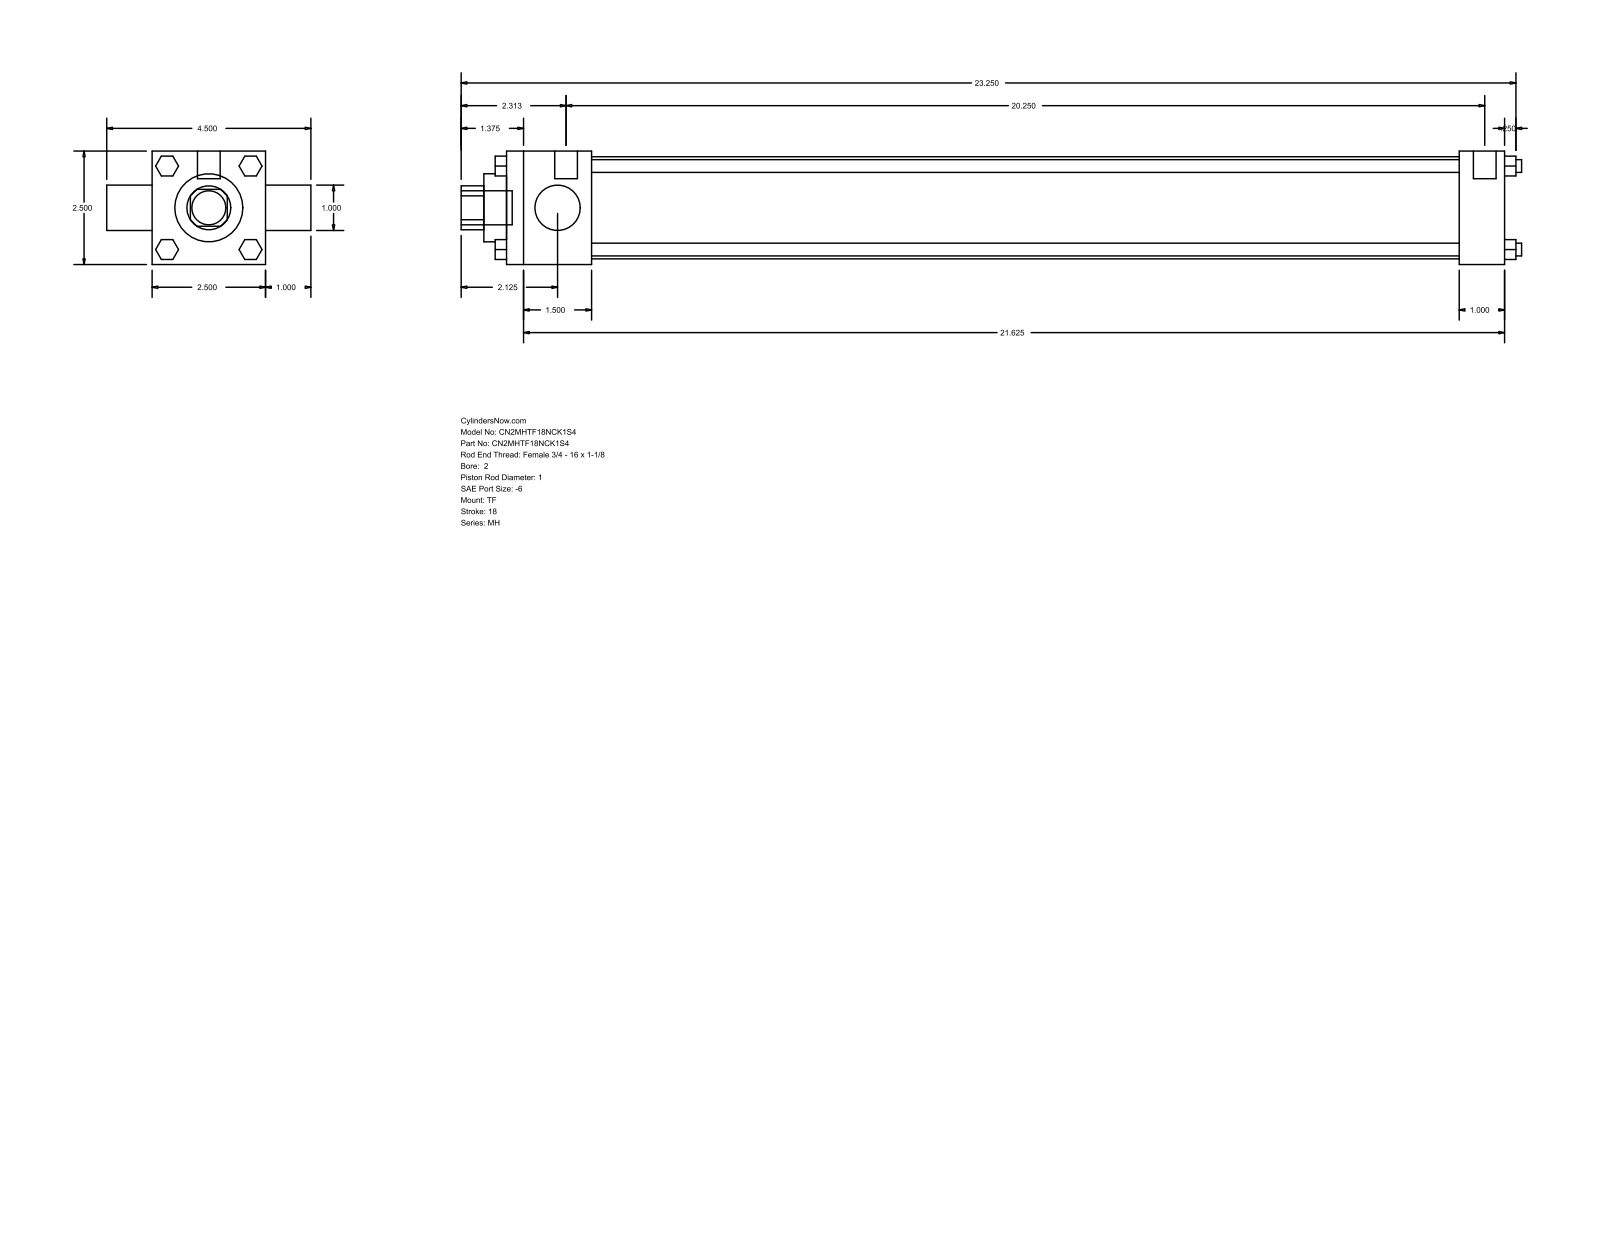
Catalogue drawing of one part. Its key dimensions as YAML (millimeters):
part_name: "MH_TF__0200_1"
step_written_by: "GSSL Pune (CONFIG_CONTROL_DESIGN)"
units: millimeters
bodies: {solids: 0, faces: 120, planar: 92, cylindrical: 28, other: 0}
overall_size: [593.73, 114.3, 63.5]
round_holes:
  - {diameter: 25.4, count: 2}
  - {diameter: 38.1, count: 1}
  - {diameter: 57.15, count: 1}
round_bosses_or_shafts:
  - {diameter: 7.14, count: 4}
  - {diameter: 5.56, count: 3}
  - {diameter: 12.7, count: 2}
  - {diameter: 19.05, count: 1}
partial_cylinders:
  - {radius: 12.29, count: 1}
face_to_face_distances: [63.5, 558.8, 25.4, 47.63, 533.4, 485.77, 511.17, 88.9, 571.5, 6.35]
